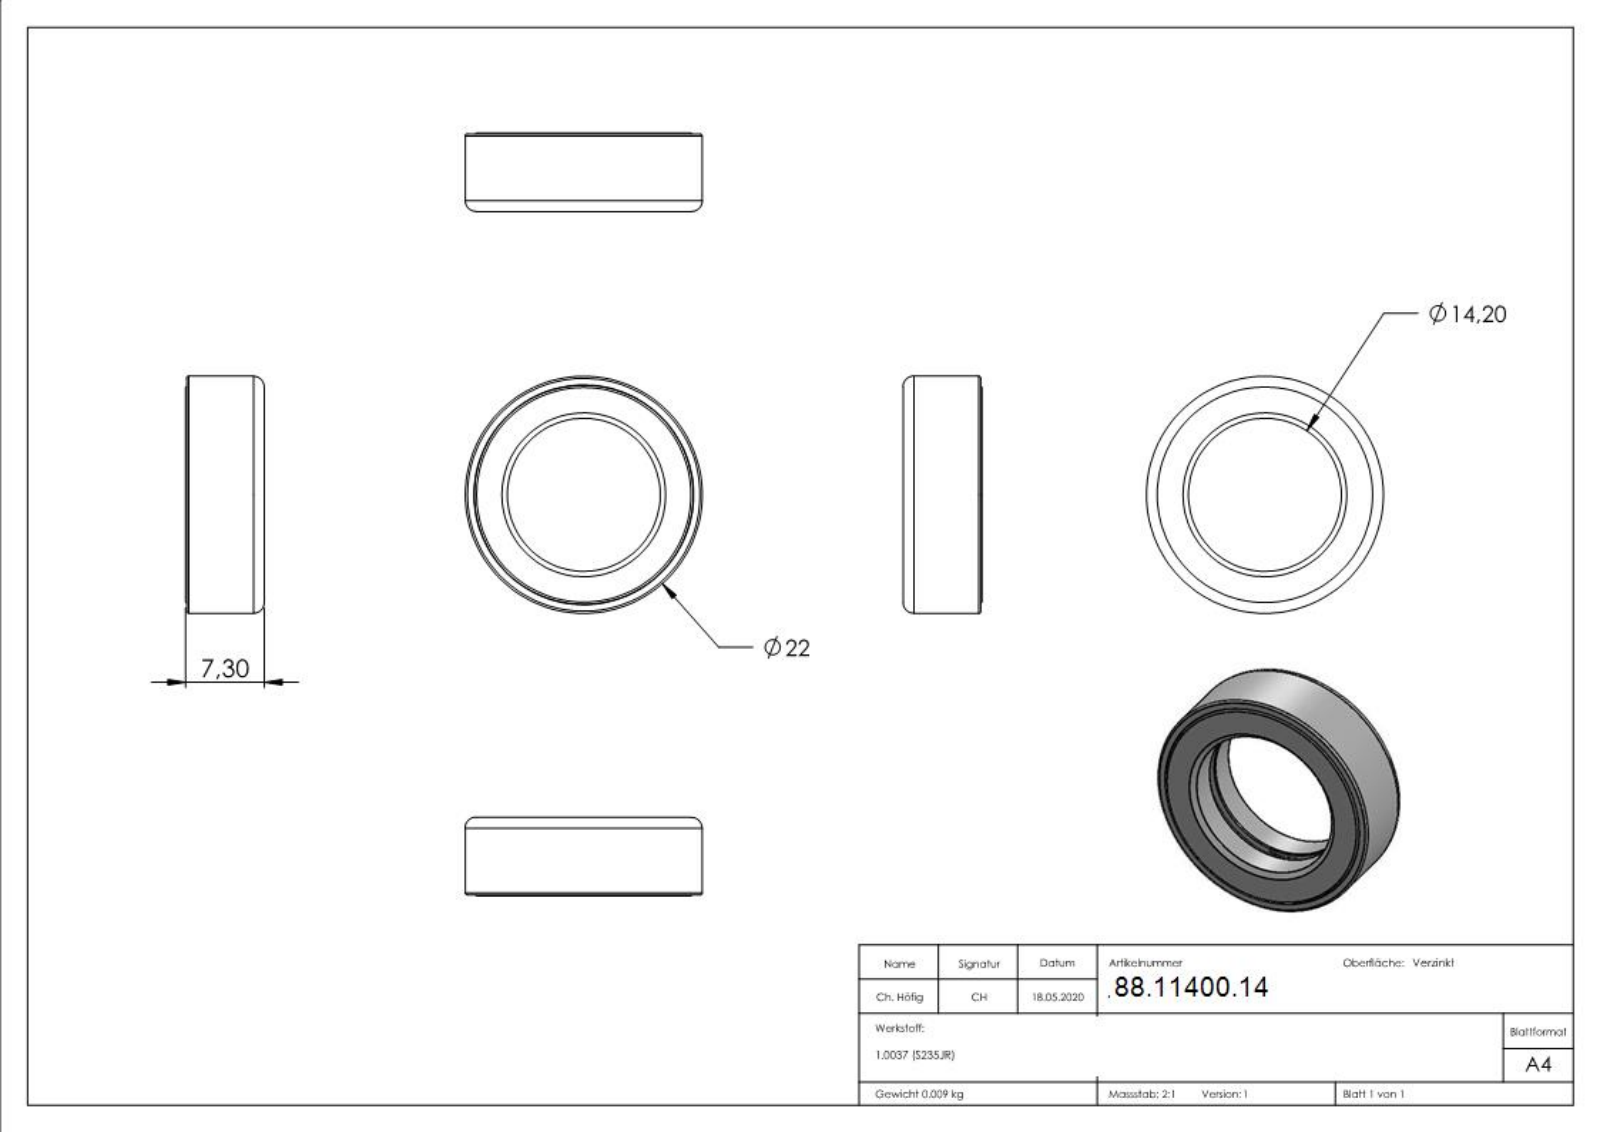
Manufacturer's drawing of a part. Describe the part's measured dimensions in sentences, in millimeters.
The part is named "400-14". Its 3-D file was written by "SolidWorks 2015 (CONFIG_CONTROL_DESIGN)". It is 28 solids with 228 faces: 119 planar, 8 cylindrical and 101 other. Overall it measures 22 by 22 by 7.3 millimeters. Its volume is 1 135 cubic millimeters and its surface area 3 079 square millimeters. Round holes: 1 of diameter 14.2, 1 of diameter 18.7, 1 of diameter 20.4. Round bosses or shafts: 1 of diameter 22, 1 of diameter 20.3, 1 of diameter 15.8. The main face-to-face distances are 0.8, 6.5, 7.3, 5.7, 4.15, 3.15, 2.35, 3.35, 0.85, 5.65.
